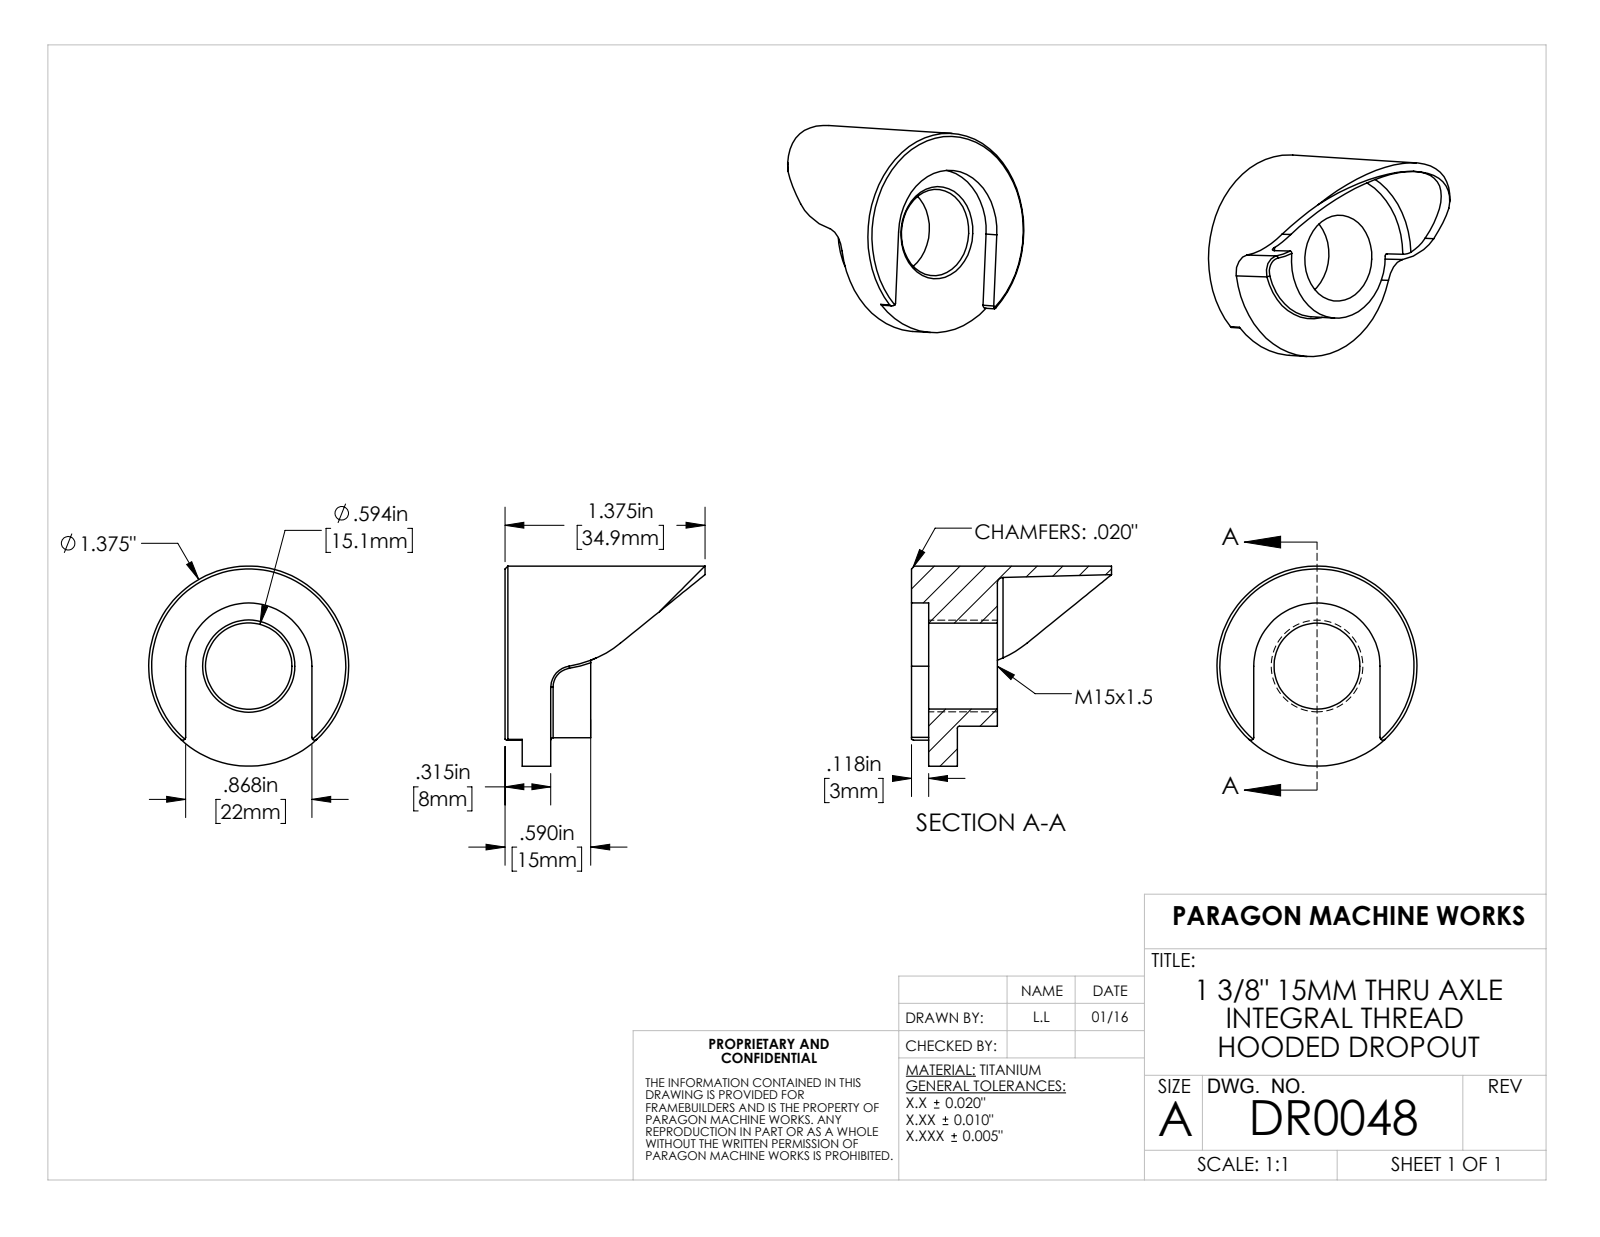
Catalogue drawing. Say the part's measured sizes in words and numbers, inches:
The part is named "DR0048-THREADED; DR0048-UNTHREADED; DR0048". Its 3-D file was written by "SolidWorks 2016 (AUTOMOTIVE_DESIGN)". It is 2 solids with 72 faces: 16 planar, 31 cylindrical and 25 other. Overall it measures 6.451 by 1.375 by 1.375 inches. Its volume is 1.212 cubic inches and its surface area 15.8 square inches. Round holes: 1 of diameter 0.591, 1 of diameter 0.594. Round bosses or shafts: 1 of diameter 1.375. Partial cylindrical surfaces (rounded edges, fillets, slot ends): 2 of radius 0.02, 2 of radius 0.15, 2 of radius 0.75, 1 of radius 0.413, 1 of radius 0.434, 1 of radius 0.492, 1 of radius 0.687, 1 of radius 0.688. The main face-to-face distances are 4.409, 0.472, 0.315, 4.016, 3.701, 3.819, 0.118, 0.59, 4.291, 0.118.
